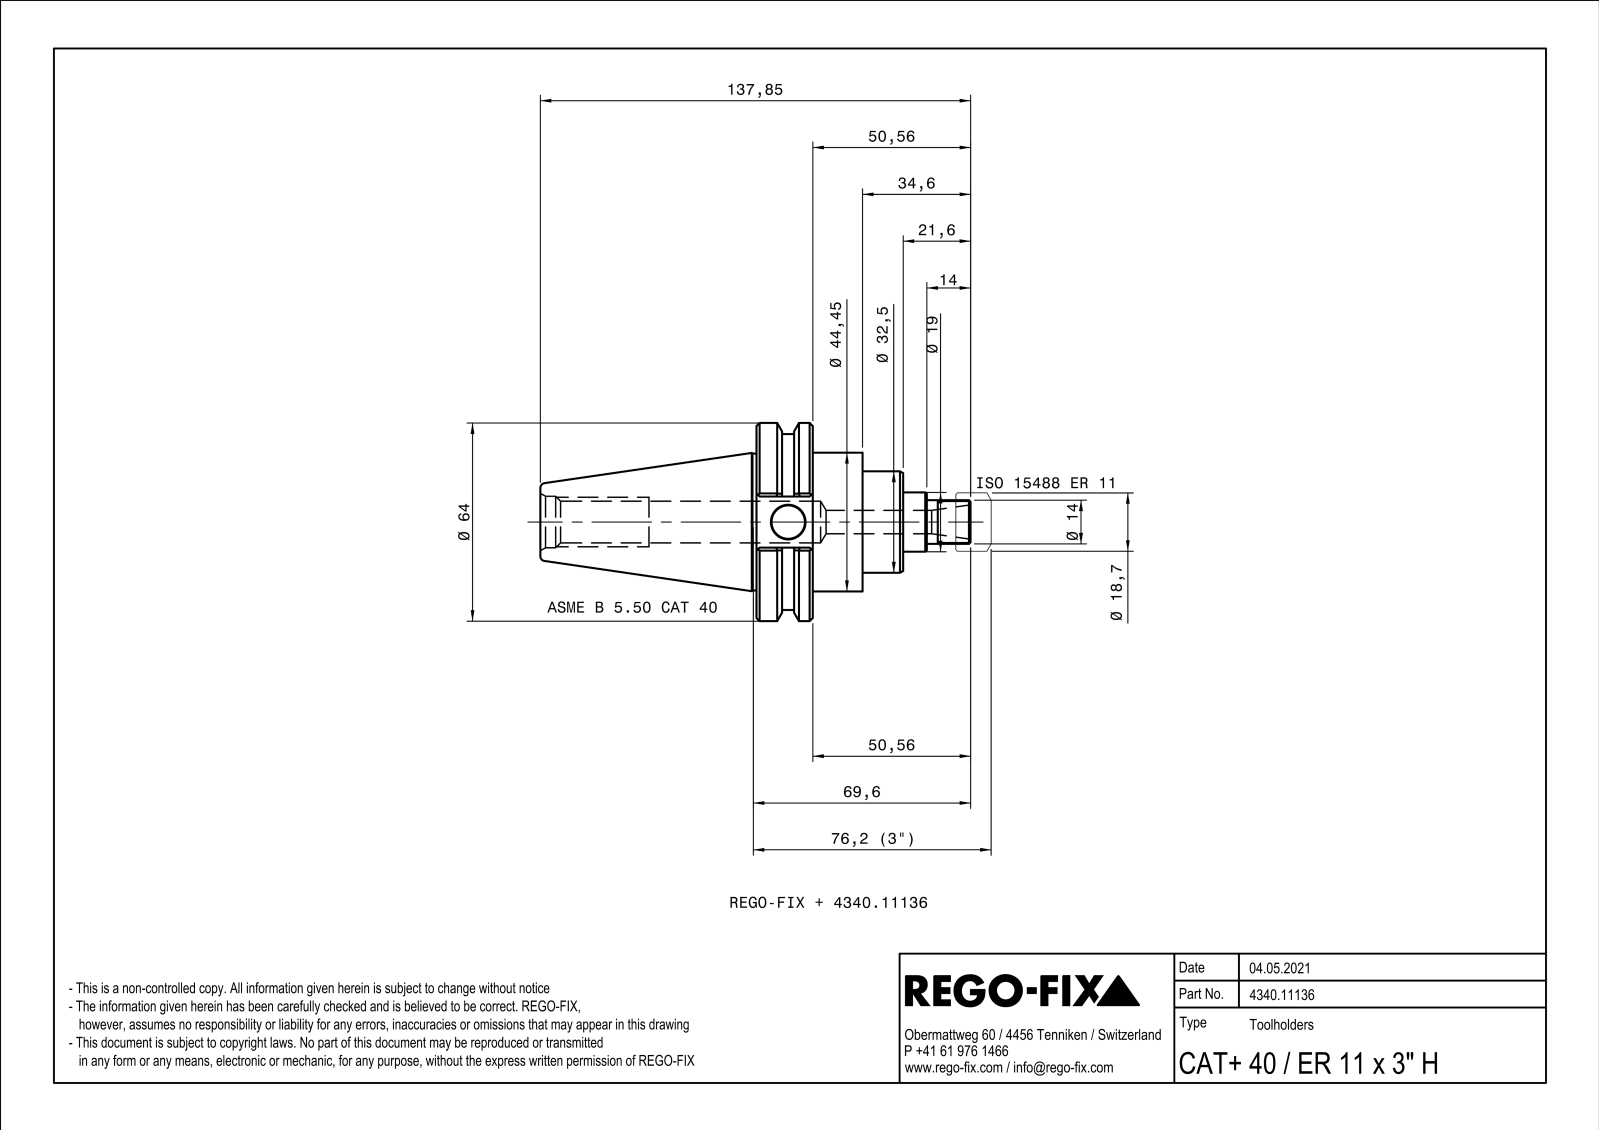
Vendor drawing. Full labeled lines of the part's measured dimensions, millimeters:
Part name (STEP PRODUCT): NOCUT
STEP written by: SIEMENS PLM Software Solid Edge ST10 (AUTOMOTIVE_DESIGN)
Units: millimetres
Bodies: 2 solids, 227 faces (74 planar, 61 cylindrical, 92 other)
Overall size (bounding box): 138.25 × 63.8 × 61.04
Volume: 281 696 mm³ · Surface area: 53 668 mm²
Round holes (diameter × count): ⌀3.9 ×2, ⌀3.24 ×1, ⌀7.5 ×1, ⌀12 ×1, ⌀13.38 ×1, ⌀16.2 ×1, ⌀16.5 ×1
Round bosses / shafts (diameter × count): ⌀63.8 ×1, ⌀63.5 ×1, ⌀56.36 ×1, ⌀44.75 ×1, ⌀44.45 ×1, ⌀43.85 ×1, ⌀32.8 ×1, ⌀32.5 ×1
Partial cylindrical surfaces — rounded edges, fillets, slot ends (radius × count): R0.5 ×4, R2.25 ×2
Main face-to-face distances: 18.05, 18.25, 34.2, 13, 47.2, 15.95, 34, 34.4, 16.15, 13.2
